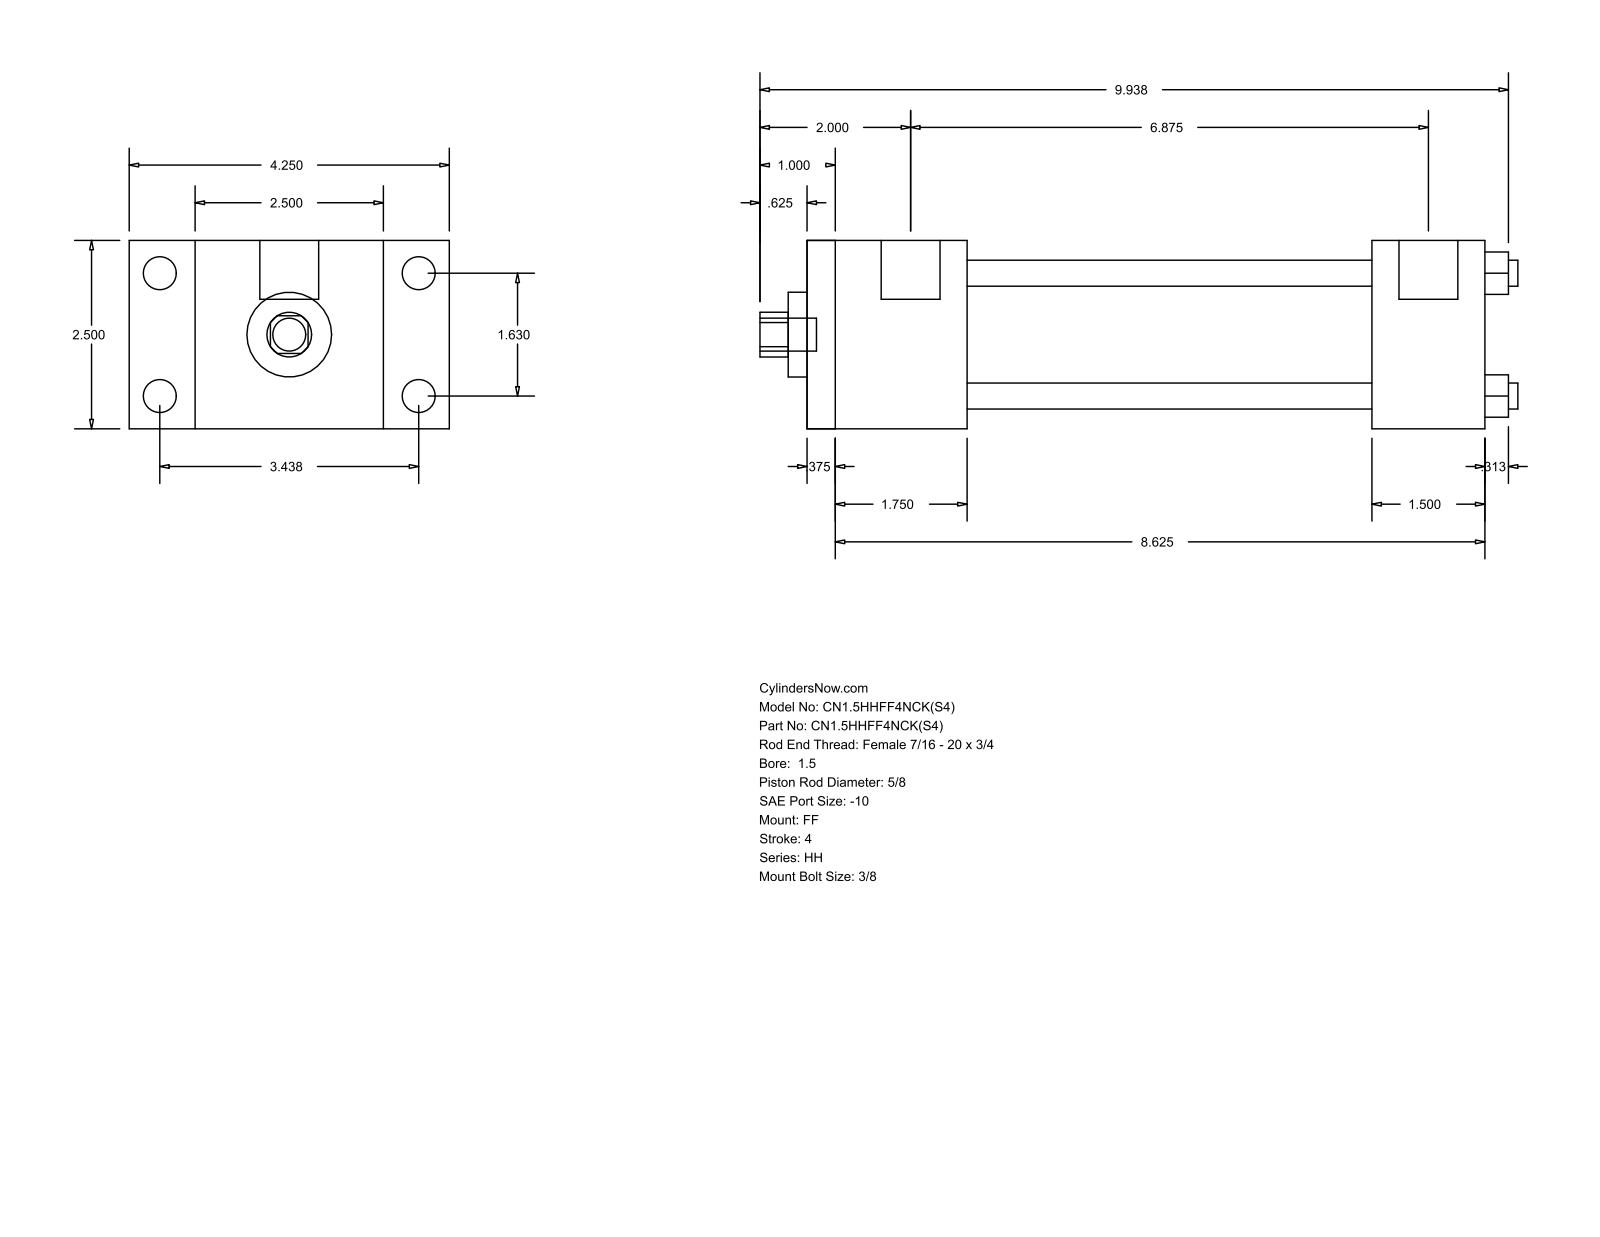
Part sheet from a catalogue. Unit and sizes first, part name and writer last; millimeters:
Units: millimetres
Overall size (bounding box): 255.59 × 107.95 × 63.5
Round holes (diameter × count): ⌀8.76 ×4, ⌀15.88 ×1, ⌀28.57 ×1, ⌀44.45 ×1
Round bosses / shafts (diameter × count): ⌀11.13 ×4, ⌀5.56 ×4, ⌀19.84 ×2, ⌀11.11 ×1
Partial cylindrical surfaces — rounded edges, fillets, slot ends (radius × count): R7.54 ×1
Main face-to-face distances: 63.5, 228.59, 9.52, 219.07, 53.97, 44.45, 174.62, 190.5, 180.98, 136.53
Hole centre spacings: 29.27, 41.4, 58.55
Bodies: 0 solids, 92 faces (64 planar, 28 cylindrical, 0 other)
Part name (STEP PRODUCT): HH_FF__0150_0.625
STEP written by: GSSL Pune (CONFIG_CONTROL_DESIGN)
